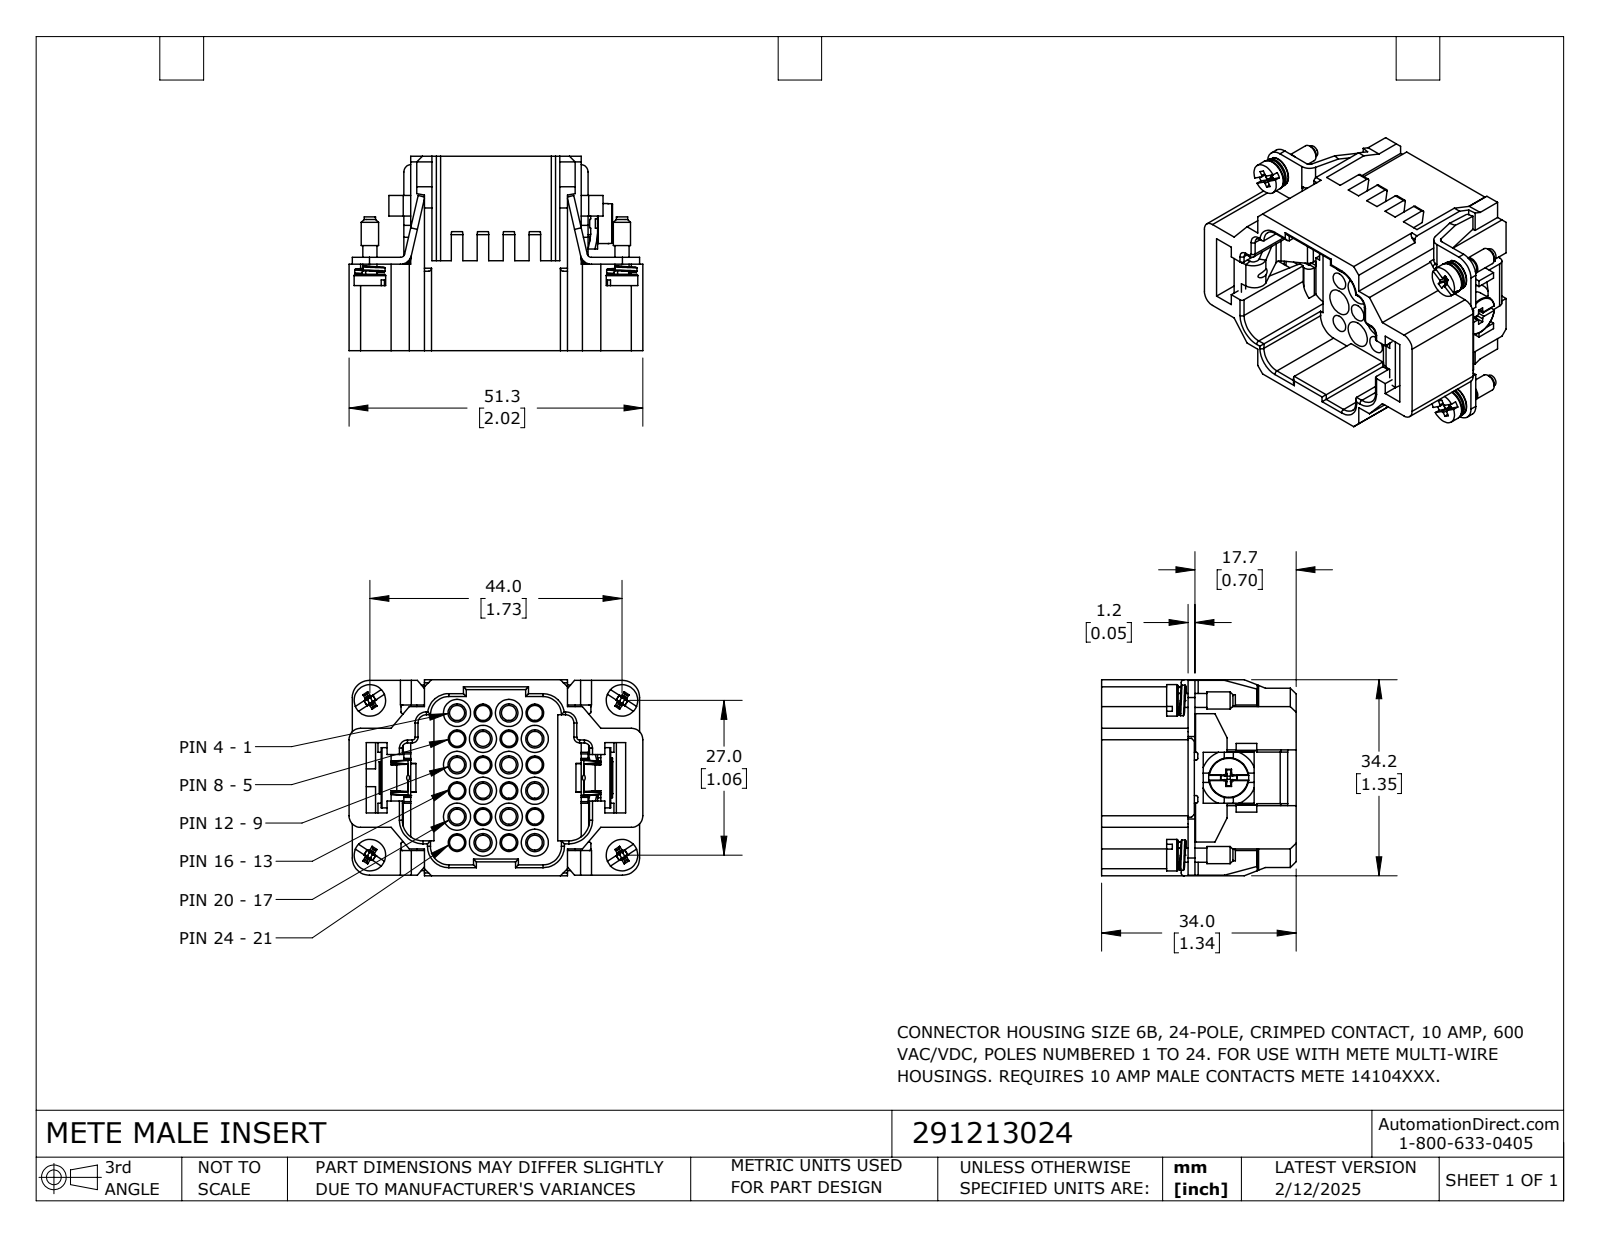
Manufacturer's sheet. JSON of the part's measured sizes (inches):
{"part_name": "291213024", "step_written_by": "SolidWorks 2024 (CONFIG_CONTROL_DESIGN)", "units": "inches", "bodies": {"solids": 13, "faces": 1279, "planar": 676, "cylindrical": 511, "other": 92}, "overall_size": [2.02, 1.347, 1.337], "volume_in3": 1.077, "surface_area_in2": 32.37, "round_holes": [[0.103, 24], [0.125, 24], [0.139, 24], [0.15, 24], [0.122, 12], [0.186, 12], [0.114, 4], [0.13, 1]], "round_bosses_or_shafts": [[0.217, 4], [0.209, 4], [0.118, 4], [0.096, 4], [0.079, 4], [0.276, 1], [0.196, 1], [0.154, 1]], "partial_cylinders_radius": [[0.01, 32], [0.02, 21], [0.012, 12], [0.004, 10], [0.051, 10], [0.006, 8], [0.02, 8], [0.053, 8]], "face_to_face_distances": [0.047, 0.115, 1.231, 0.075, 0.594, 0.067, 0.071, 0.095, 0.915, 0.148], "hole_center_spacings": [0.178, 0.398, 0.564, 0.643, 0.535, 0.252, 0.399, 0.356]}
